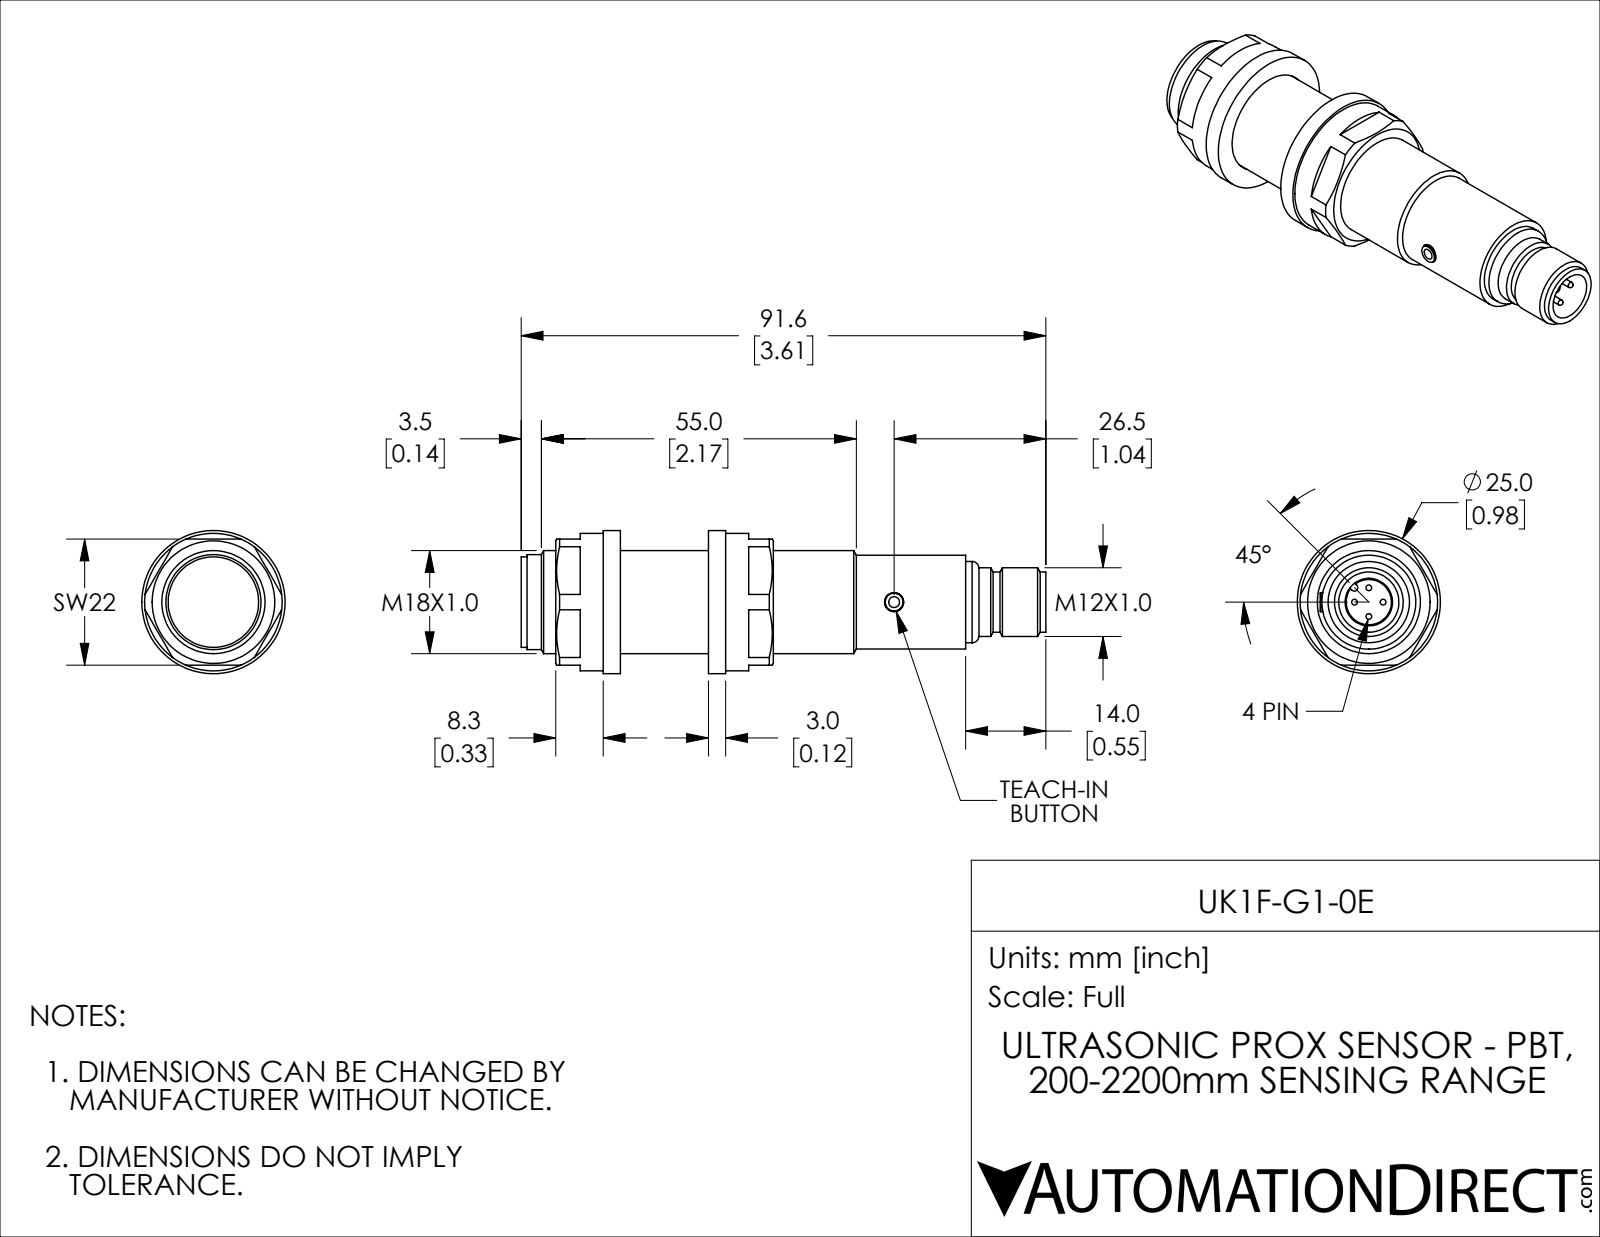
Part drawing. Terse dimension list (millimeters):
name: UK1F-G1-0E
written by: SolidWorks 2018 (AUTOMOTIVE_DESIGN)
unit: mm
bodies: 6 solids, 123 faces (43 planar, 49 cylindrical, 31 other)
size: 91.6 × 25 × 25
volume: 24 200 mm³; area: 10 330 mm²
holes: 1× ⌀3.3, 1× ⌀8.3, 1× ⌀18, 1× ⌀18.2
bosses: 4× ⌀1, 1× ⌀25, 1× ⌀24, 1× ⌀16.6, 1× ⌀16.4, 1× ⌀15.8, 1× ⌀14.2, 1× ⌀12
rounds: 1× R0.6
face distances: 3, 18.4, 21.4, 15.4, 22, 8.3, 11.3, 26.7, 29.7, 14.3
